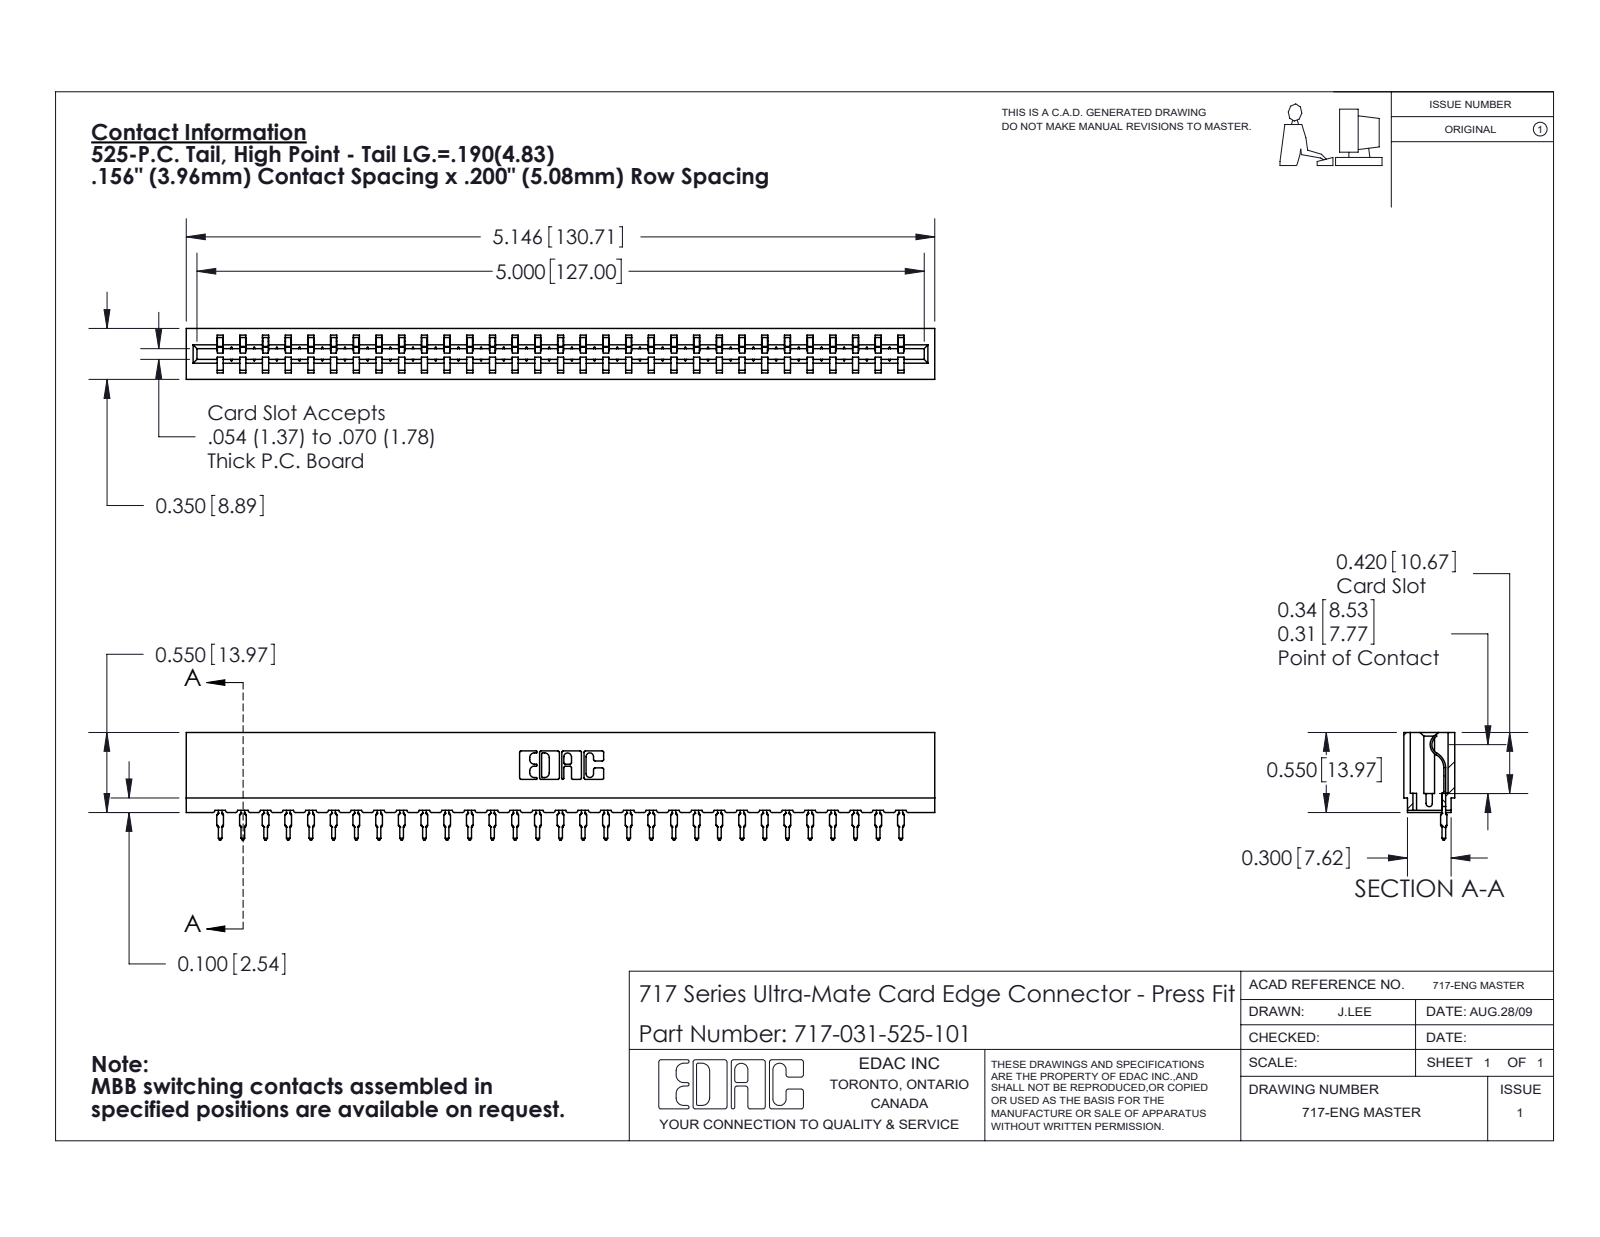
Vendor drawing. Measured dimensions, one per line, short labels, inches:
name: 745-292-001_525; 717-031-525-101; 717 Part_Insulator Option - 06
written by: SolidWorks 2020 (CONFIG_CONTROL_DESIGN)
unit: in
bodies: 32 solids, 3597 faces (2162 planar, 629 cylindrical, 806 other)
size: 5.146 × 0.739 × 0.35
volume: 0.675 in³; area: 23.75 in²
rounds: 62× R0.015, 62× R0.021, 22× R0.01, 6× R0.007, 6× R0.031, 4× R0.005, 4× R0.011, 3× R0.026
face distances: 0.212, 0.138, 0.35, 0.074, 0.045, 0.305, 0.093, 0.167, 0.025, 0.156
